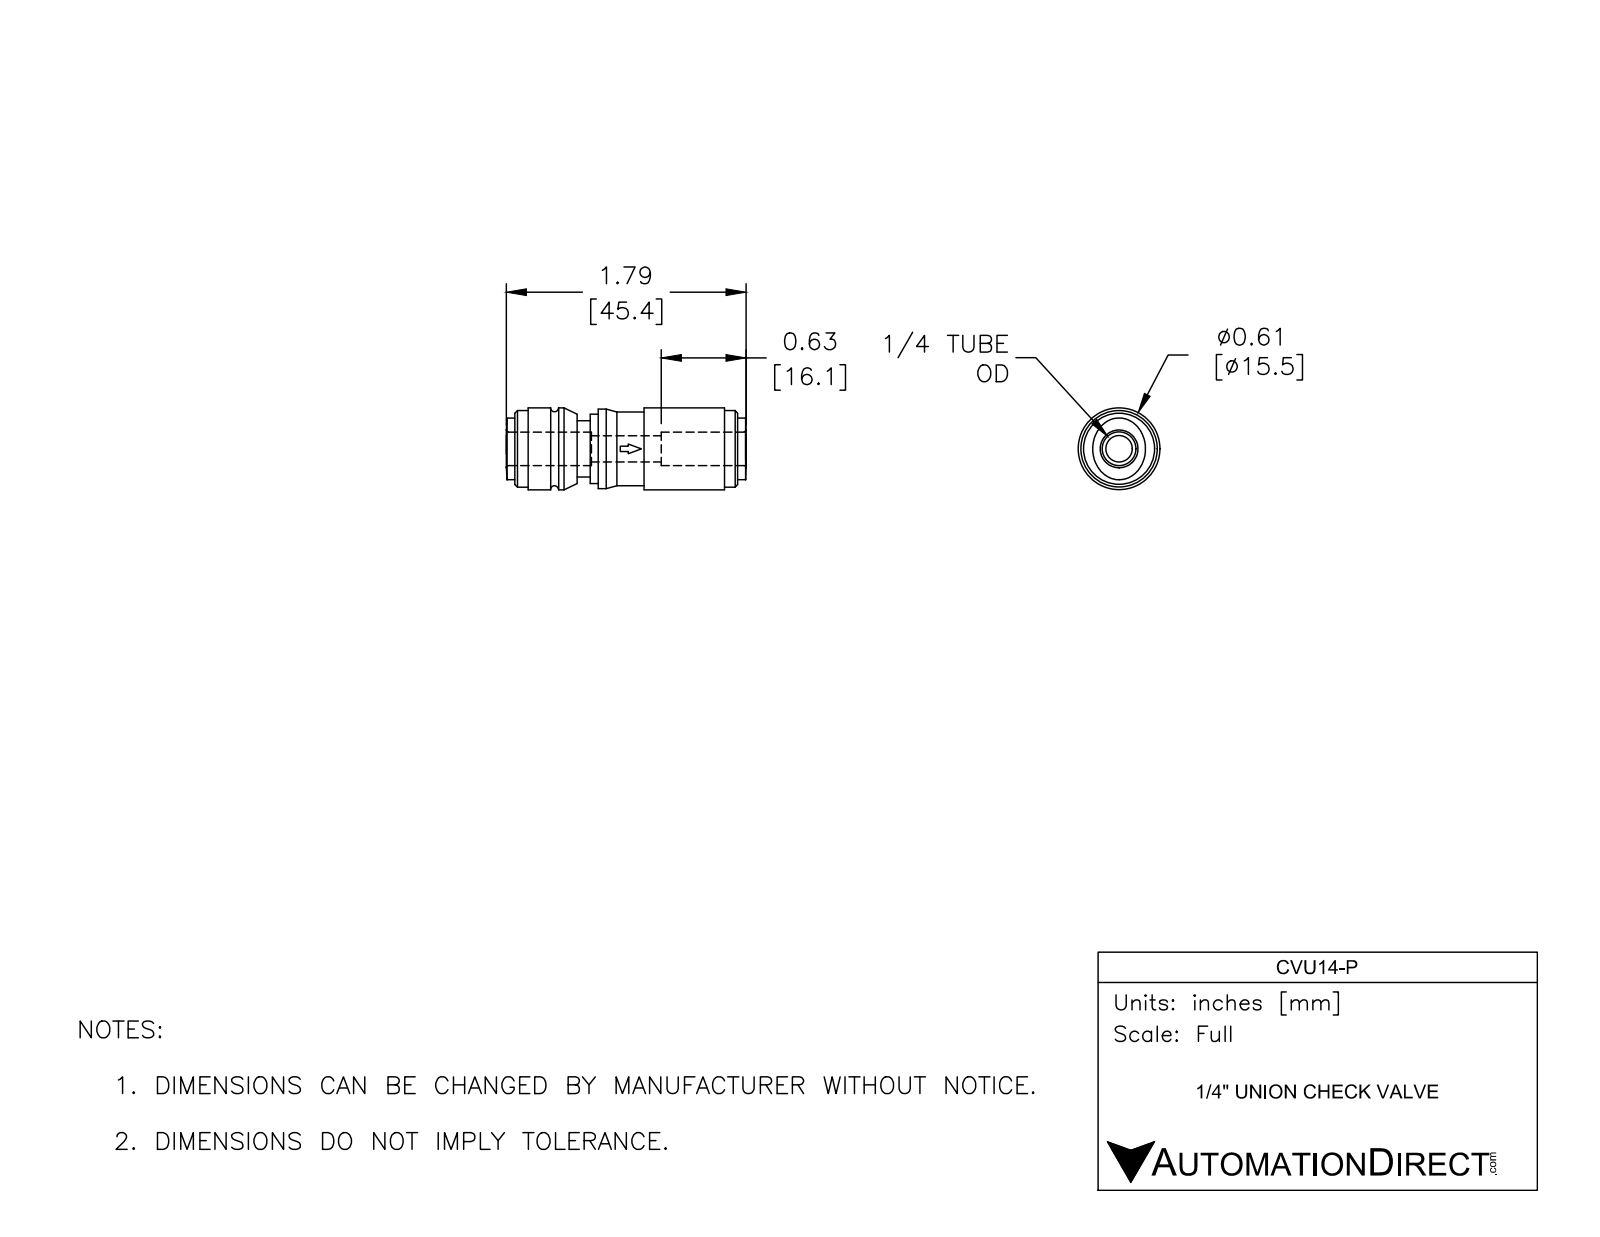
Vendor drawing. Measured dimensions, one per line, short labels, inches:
name: CVU14-P
written by: SolidWorks 2017 (AUTOMOTIVE_DESIGN)
unit: in
bodies: 1 solid, 66 faces (17 planar, 25 cylindrical, 24 other)
size: 1.789 × 0.61 × 0.61
volume: 0.377 in³; area: 5.313 in²
holes: 1× ⌀0.197, 1× ⌀0.25
bosses: 1× ⌀0.61, 1× ⌀0.594, 1× ⌀0.571, 1× ⌀0.551, 1× ⌀0.518, 1× ⌀0.421
rounds: 1× R0.28
face distances: 1.663, 0.098, 1.565, 1.198, 0.465, 1.1, 0.098, 0.563, 0.059, 1.041
